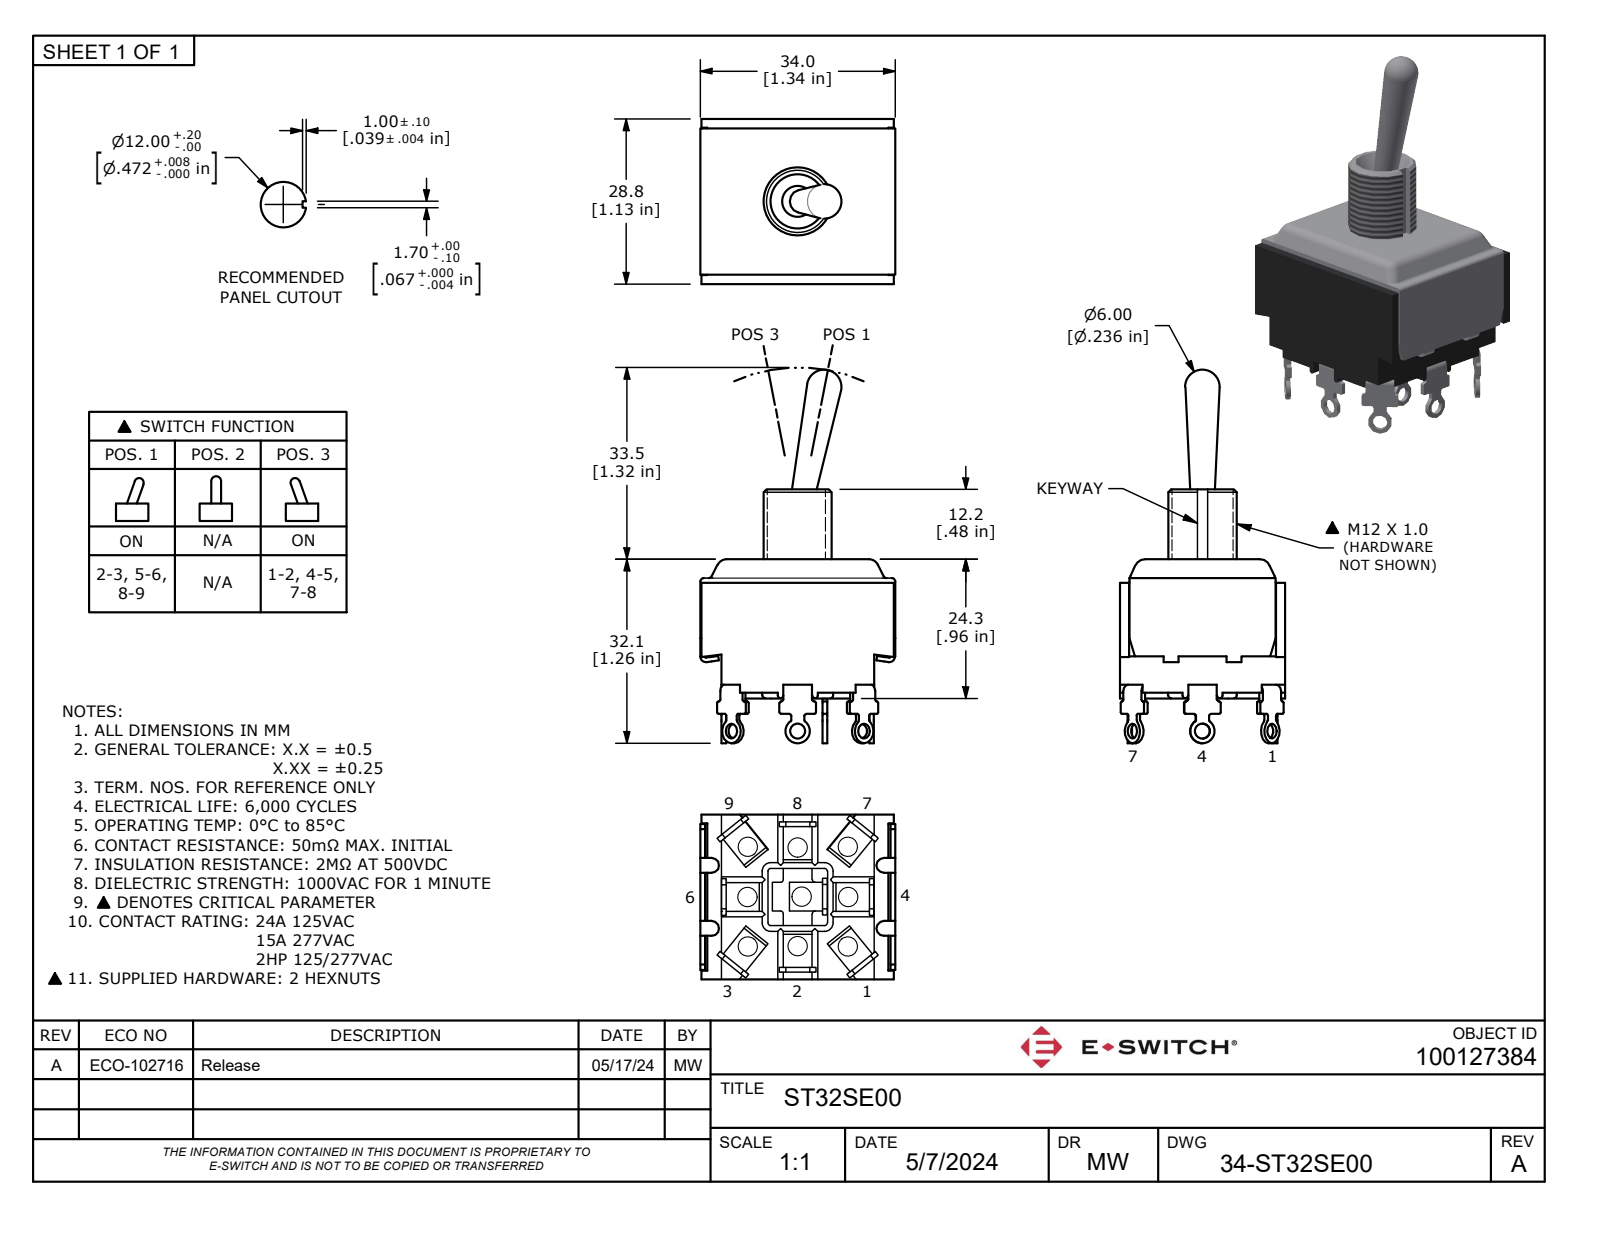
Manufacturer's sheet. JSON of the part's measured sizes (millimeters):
{"part_name": "ST32SE00", "step_written_by": "Autodesk Inventor 2022 (AUTOMOTIVE_DESIGN)", "units": "millimeters", "bodies": {"solids": 1, "faces": 573, "planar": 324, "cylindrical": 186, "other": 63}, "overall_size": [65.16, 34, 28.8], "volume_mm3": 21736, "surface_area_mm2": 8428, "round_holes": [[2, 9], [2.6, 7], [5.4, 1]], "round_bosses_or_shafts": [[11.91, 1]], "partial_cylinders_radius": [[0.3, 79], [0.5, 16], [1.1, 9], [2.1, 7], [1.75, 6], [0.6, 4], [1.3, 4], [1.5, 4]], "face_to_face_distances": [0.8, 1.2, 0.4, 32.8, 33.2, 32, 28.8, 2.45, 3.65, 30.35], "hole_center_spacings": [12.3, 8.75, 2.66, 8.6, 8.64, 8.74, 8.8, 11.88]}
